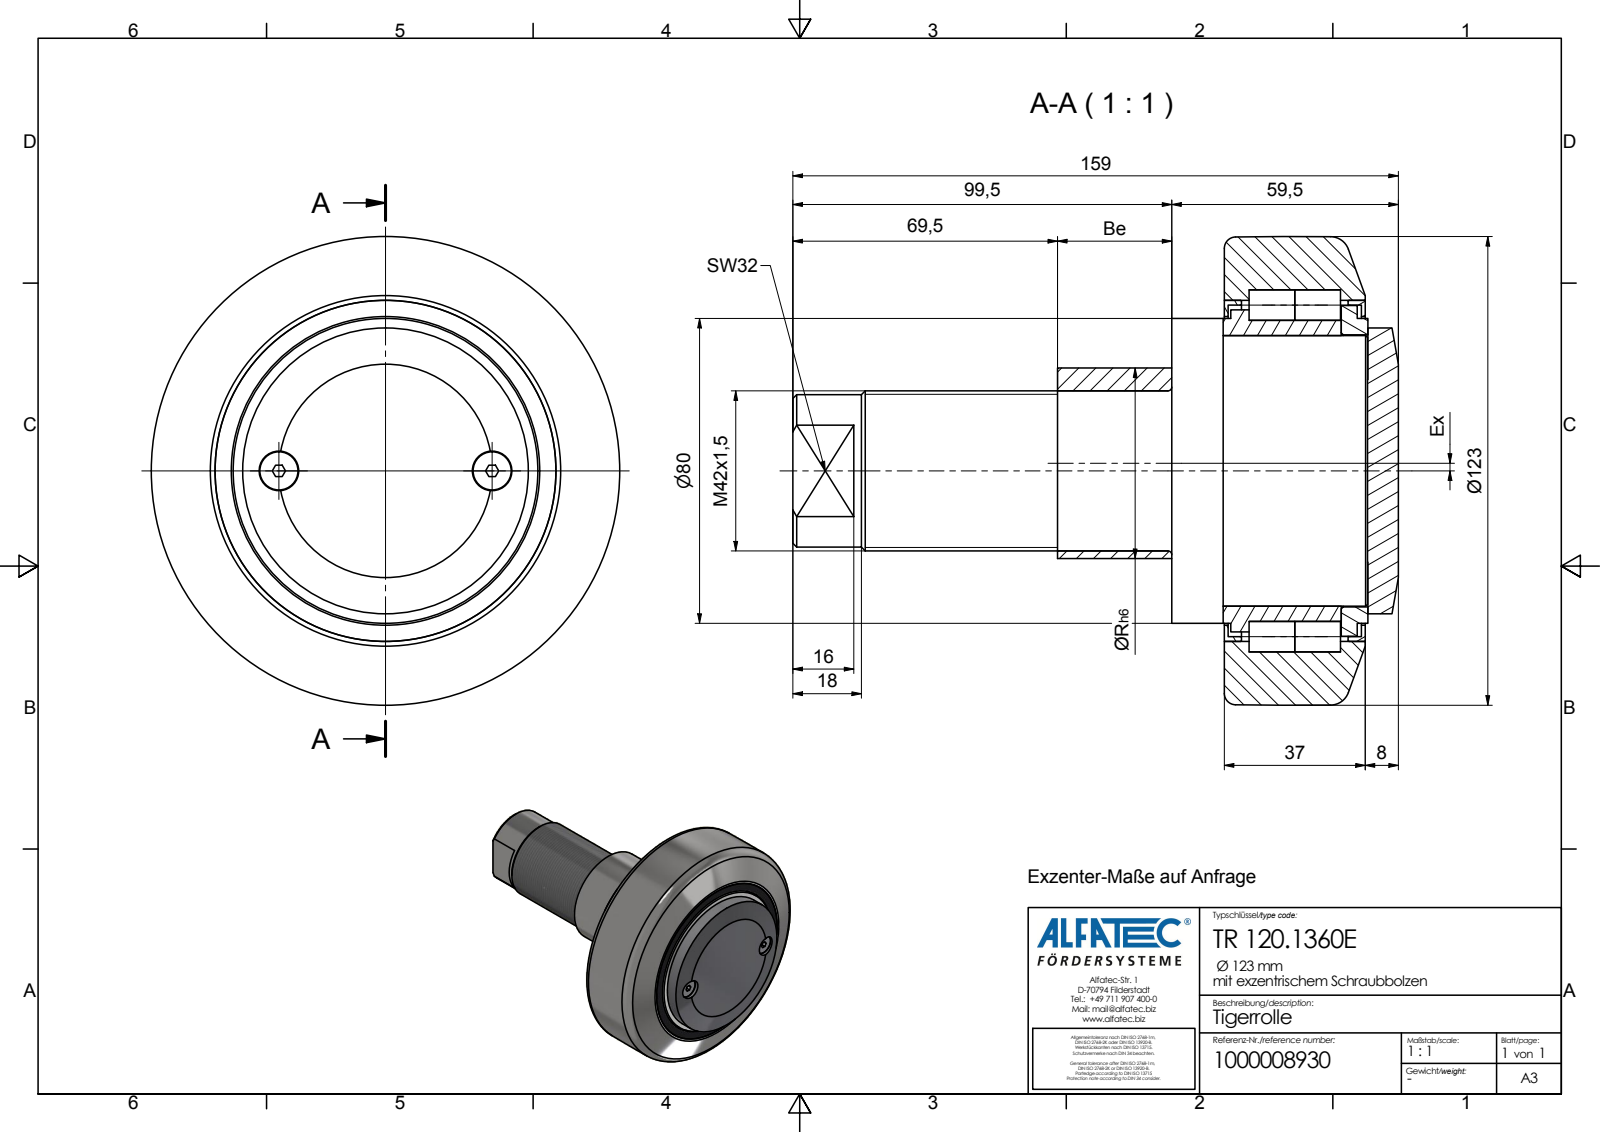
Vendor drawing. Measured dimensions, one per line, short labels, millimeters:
name: TR 120.1360E_Kontur
written by: Autodesk Inventor 2020 (AUTOMOTIVE_DESIGN)
unit: mm
bodies: 2 solids, 73 faces (37 planar, 24 cylindrical, 12 other)
size: 159 × 123 × 123
volume: 621 199 mm³; area: 81 476 mm²
holes: 2× ⌀10.4, 1× ⌀3, 1× ⌀81, 1× ⌀87, 1× ⌀89.5, 1× ⌀95
bosses: 2× ⌀10, 1× ⌀86.8, 1× ⌀84.5, 1× ⌀80, 1× ⌀79, 1× ⌀75, 1× ⌀50, 1× ⌀42
rounds: 1× R35.5
face distances: 13.8, 59.5, 45.7, 6.5, 30.5, 36, 5.5, 1, 29.5, 37
hole spacings: 28, 56
